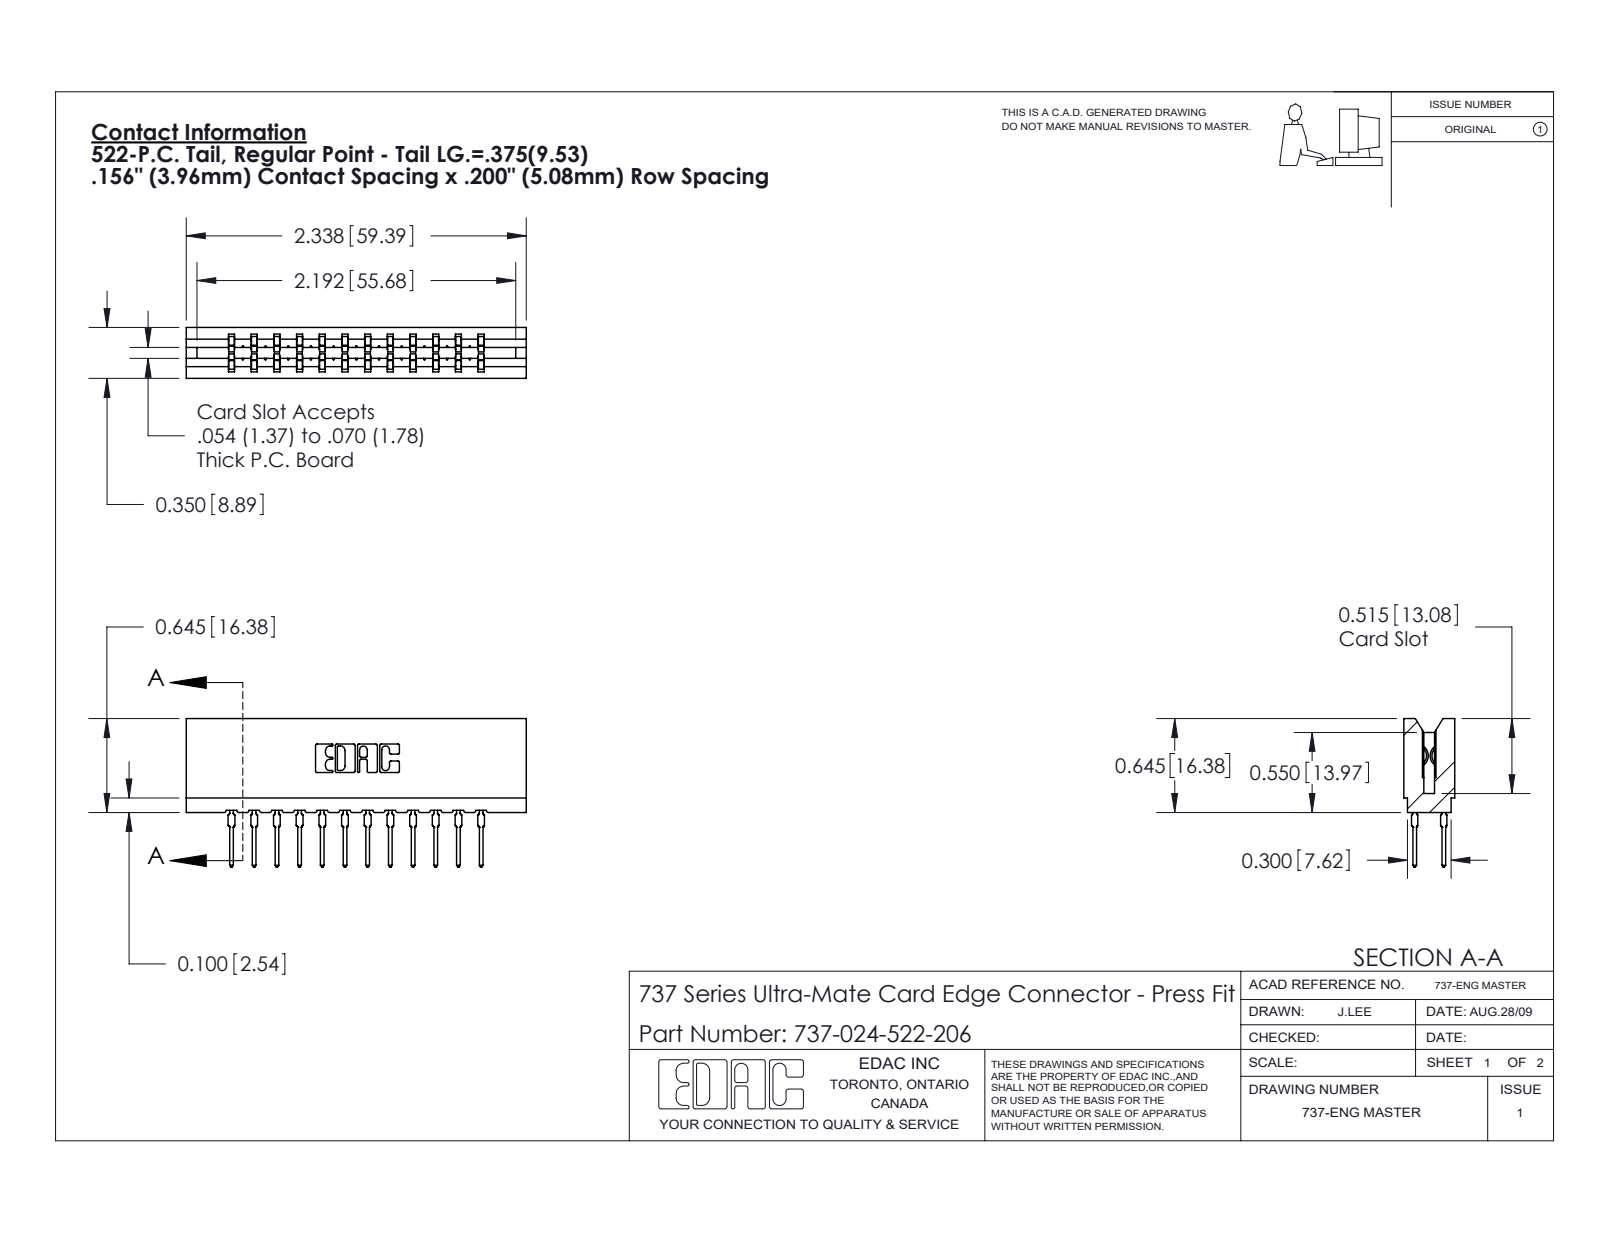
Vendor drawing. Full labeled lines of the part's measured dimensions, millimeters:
Part name (STEP PRODUCT): 737-024-522-206; 737 Part_Insulator Option - 06; 745-292-001_522
STEP written by: SolidWorks 2020 (CONFIG_CONTROL_DESIGN)
Units: millimetres
Bodies: 25 solids, 2255 faces (1171 planar, 460 cylindrical, 624 other)
Overall size (bounding box): 59.4 × 25.9 × 8.9
Volume: 6 060 mm³ · Surface area: 8 252 mm²
Partial cylindrical surfaces — rounded edges, fillets, slot ends (radius × count): R0.5 ×48, R0.4 ×24, R0.3 ×22, R0.1 ×8, R0.3 ×8, R0.2 ×6, R0.8 ×6, R0.7 ×3
Main face-to-face distances: 4, 3.5, 5.4, 8.9, 15.8, 7.9, 11.9, 19.8, 1.9, 9
